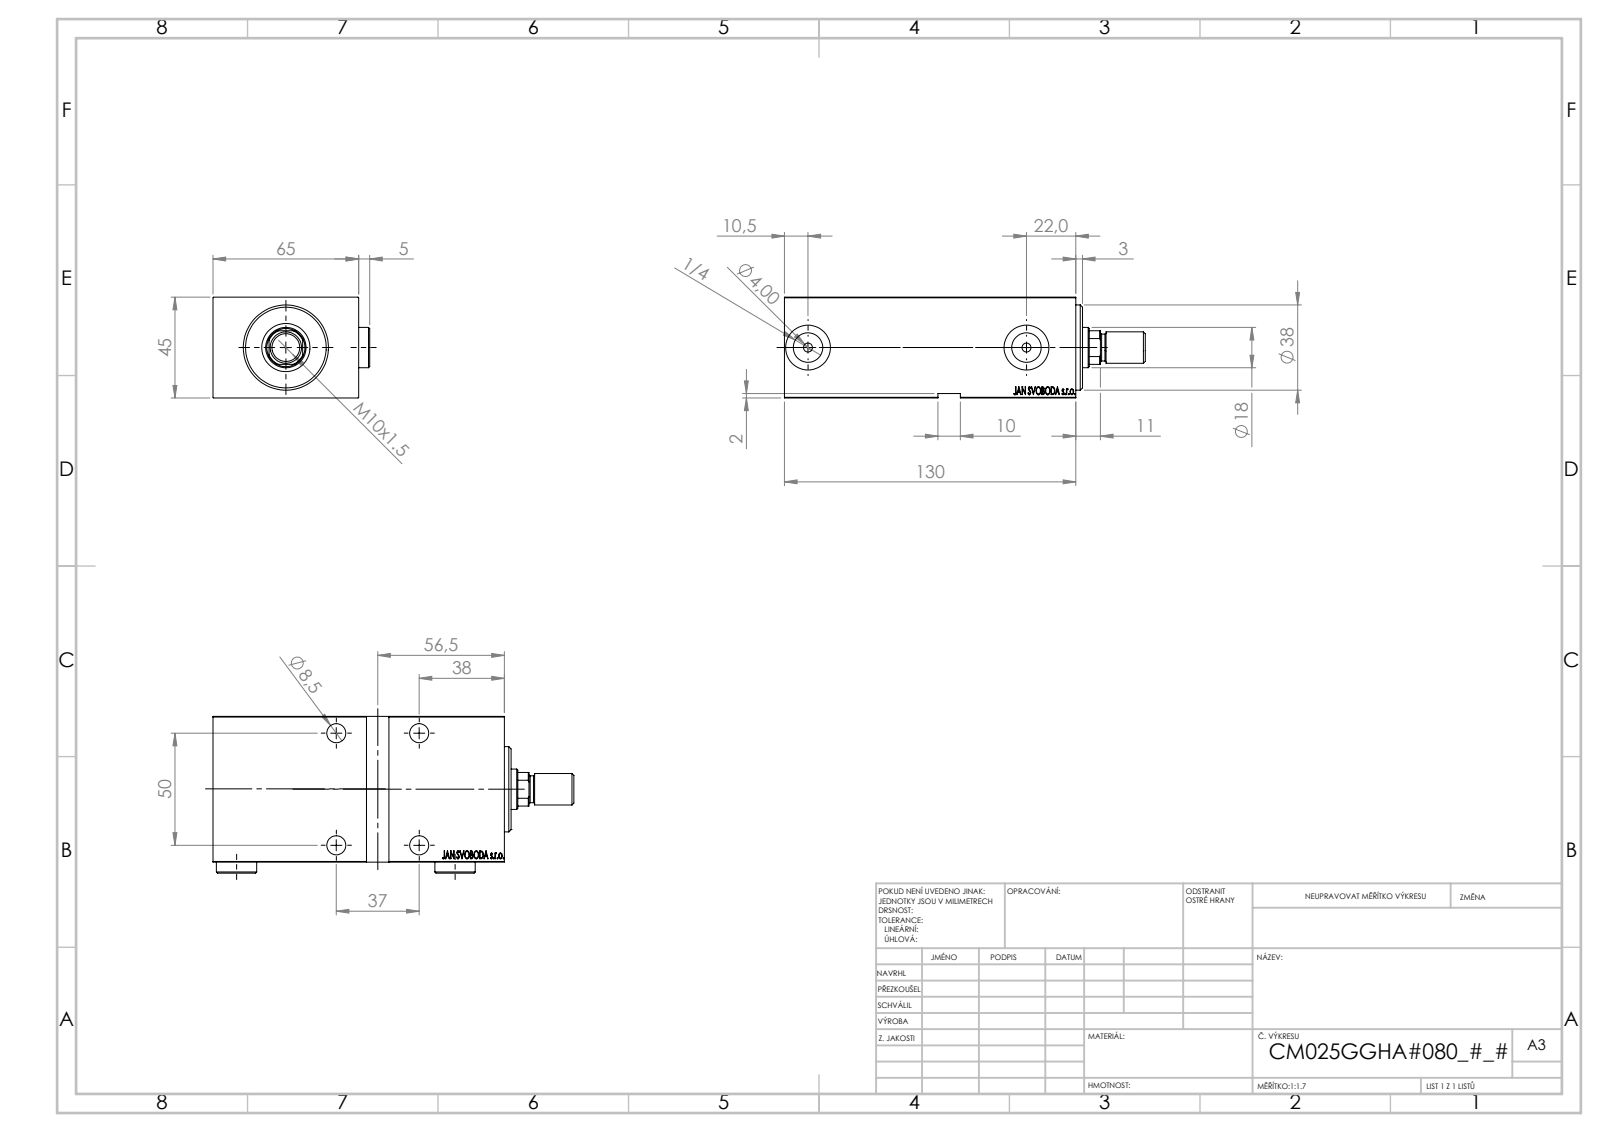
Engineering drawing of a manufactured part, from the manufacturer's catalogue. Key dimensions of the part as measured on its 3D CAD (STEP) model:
Part name (STEP PRODUCT): V450CM_MALE_METRIC; Zatka_OIL_PORT; V450CM_VC_G; V450CM_G_VCP (+1 more)
STEP written by: SolidWorks 2019 (CONFIG_CONTROL_DESIGN)
Units: millimetres
Bodies: 6 solids, 910 faces (444 planar, 62 cylindrical, 404 other)
Overall size (bounding box): 161 × 69.9 × 45
Volume: 351 248 mm³ · Surface area: 67 364 mm²
Round holes (diameter × count): ⌀8.5 ×5, ⌀13.5 ×4, ⌀4 ×2, ⌀13.16 ×2, ⌀20 ×2, ⌀18 ×1, ⌀21.5 ×1, ⌀25 ×1, ⌀27 ×1, ⌀35 ×1
Round bosses / shafts (diameter × count): ⌀18 ×2, ⌀38 ×1, ⌀14 ×1, ⌀12 ×1
Partial cylindrical surfaces — rounded edges, fillets, slot ends (radius × count): R8.5 ×1
Main face-to-face distances: 45, 65, 130, 6, 119, 5, 124, 8, 64.9, 125
Hole centre spacings: 37, 50, 62.2, 97.5
